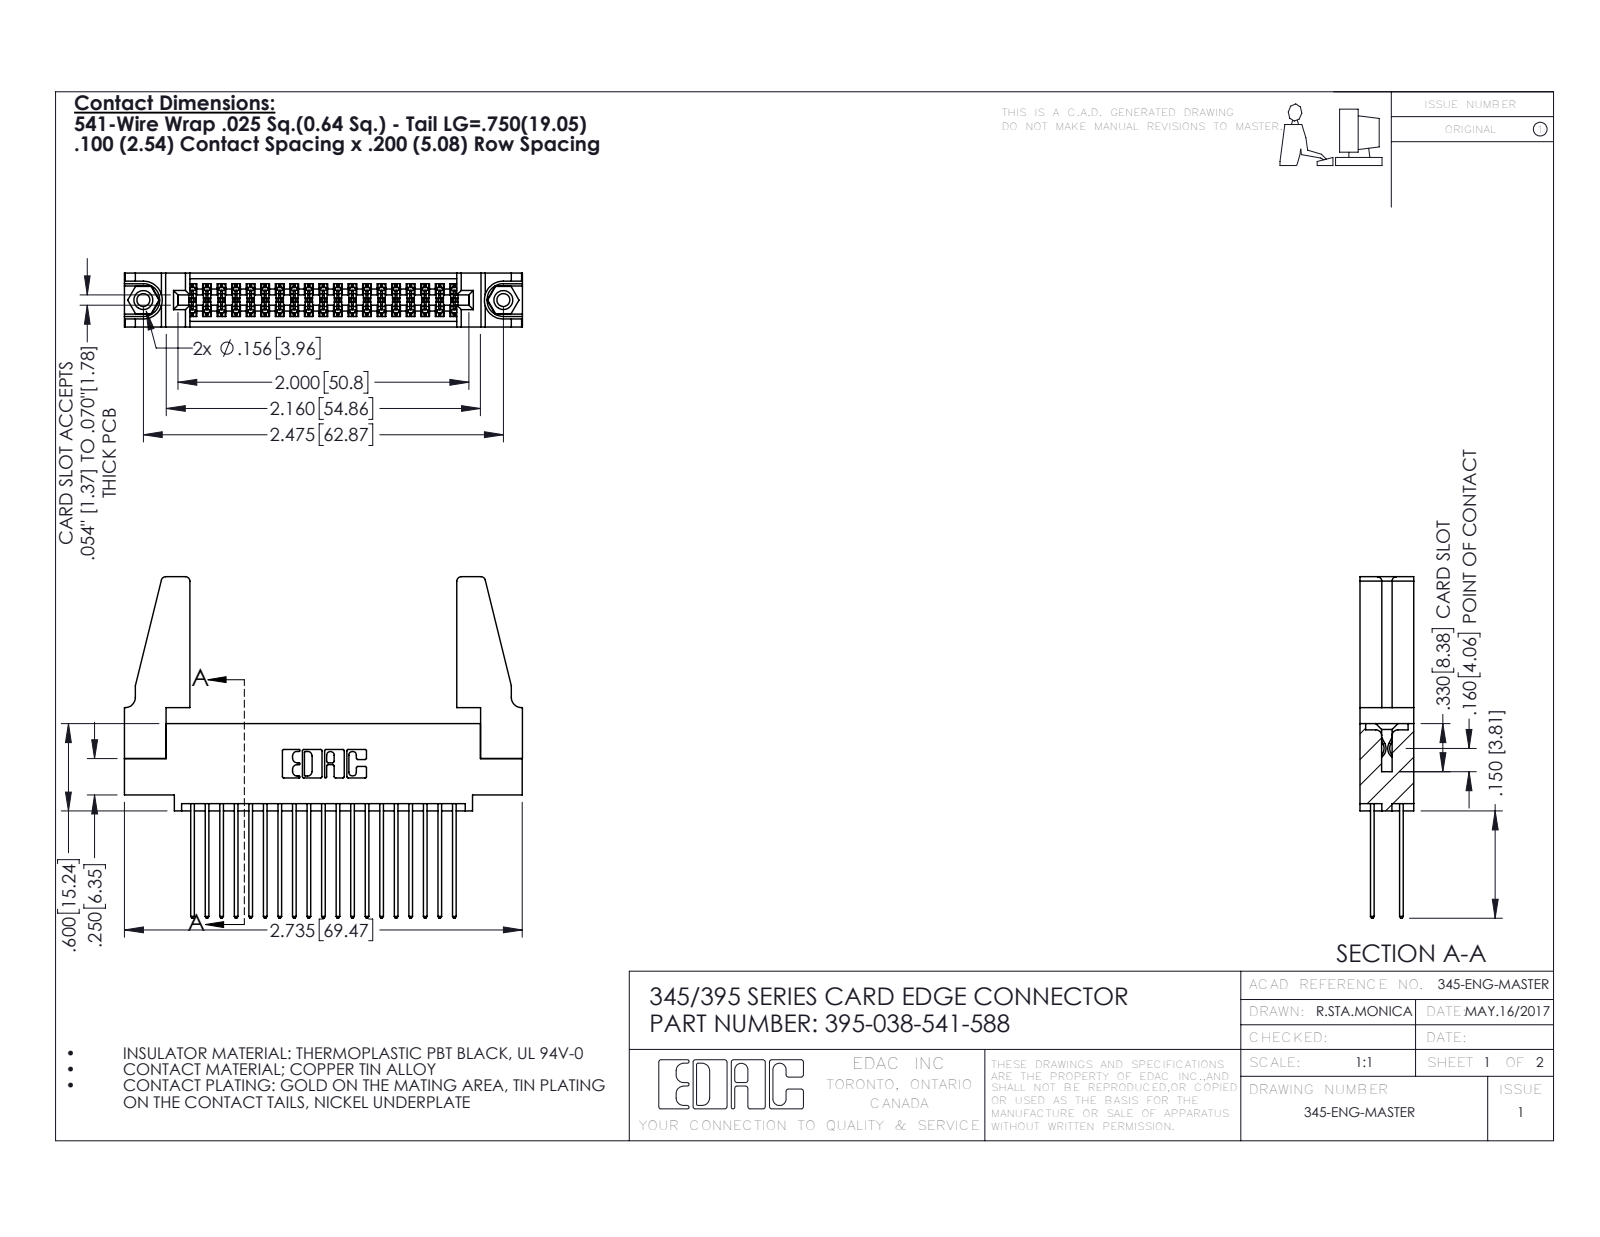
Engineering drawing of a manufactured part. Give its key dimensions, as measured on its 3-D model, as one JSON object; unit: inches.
{"part_name": "345-292-001_345-293-141; 395-038-541-588; 345 Part_0.110 Offset - 0.156 Dia-TH; 345-250-001_345-250-001-102 (+1 more)", "step_written_by": "SolidWorks 2016 (CONFIG_CONTROL_DESIGN)", "units": "inches", "bodies": {"solids": 43, "faces": 2154, "planar": 1410, "cylindrical": 728, "other": 16}, "overall_size": [2.736, 2.347, 0.37], "volume_in3": 0.606, "surface_area_in2": 21.19, "round_holes": [[0.089, 2], [0.125, 2], [0.156, 2], [0.064, 1]], "round_bosses_or_shafts": [[0.155, 2]], "partial_cylinders_radius": [[0.006, 57], [0.01, 38], [0.01, 22], [0.03, 8], [0.007, 6], [0.031, 6], [0.026, 3], [0.014, 2]], "face_to_face_distances": [0.072, 0.298, 0.37, 0.2, 0.098, 0.272, 0.025, 0.225, 0.175, 0.148], "hole_center_spacings": [0.27, 2.241, 2.475]}
